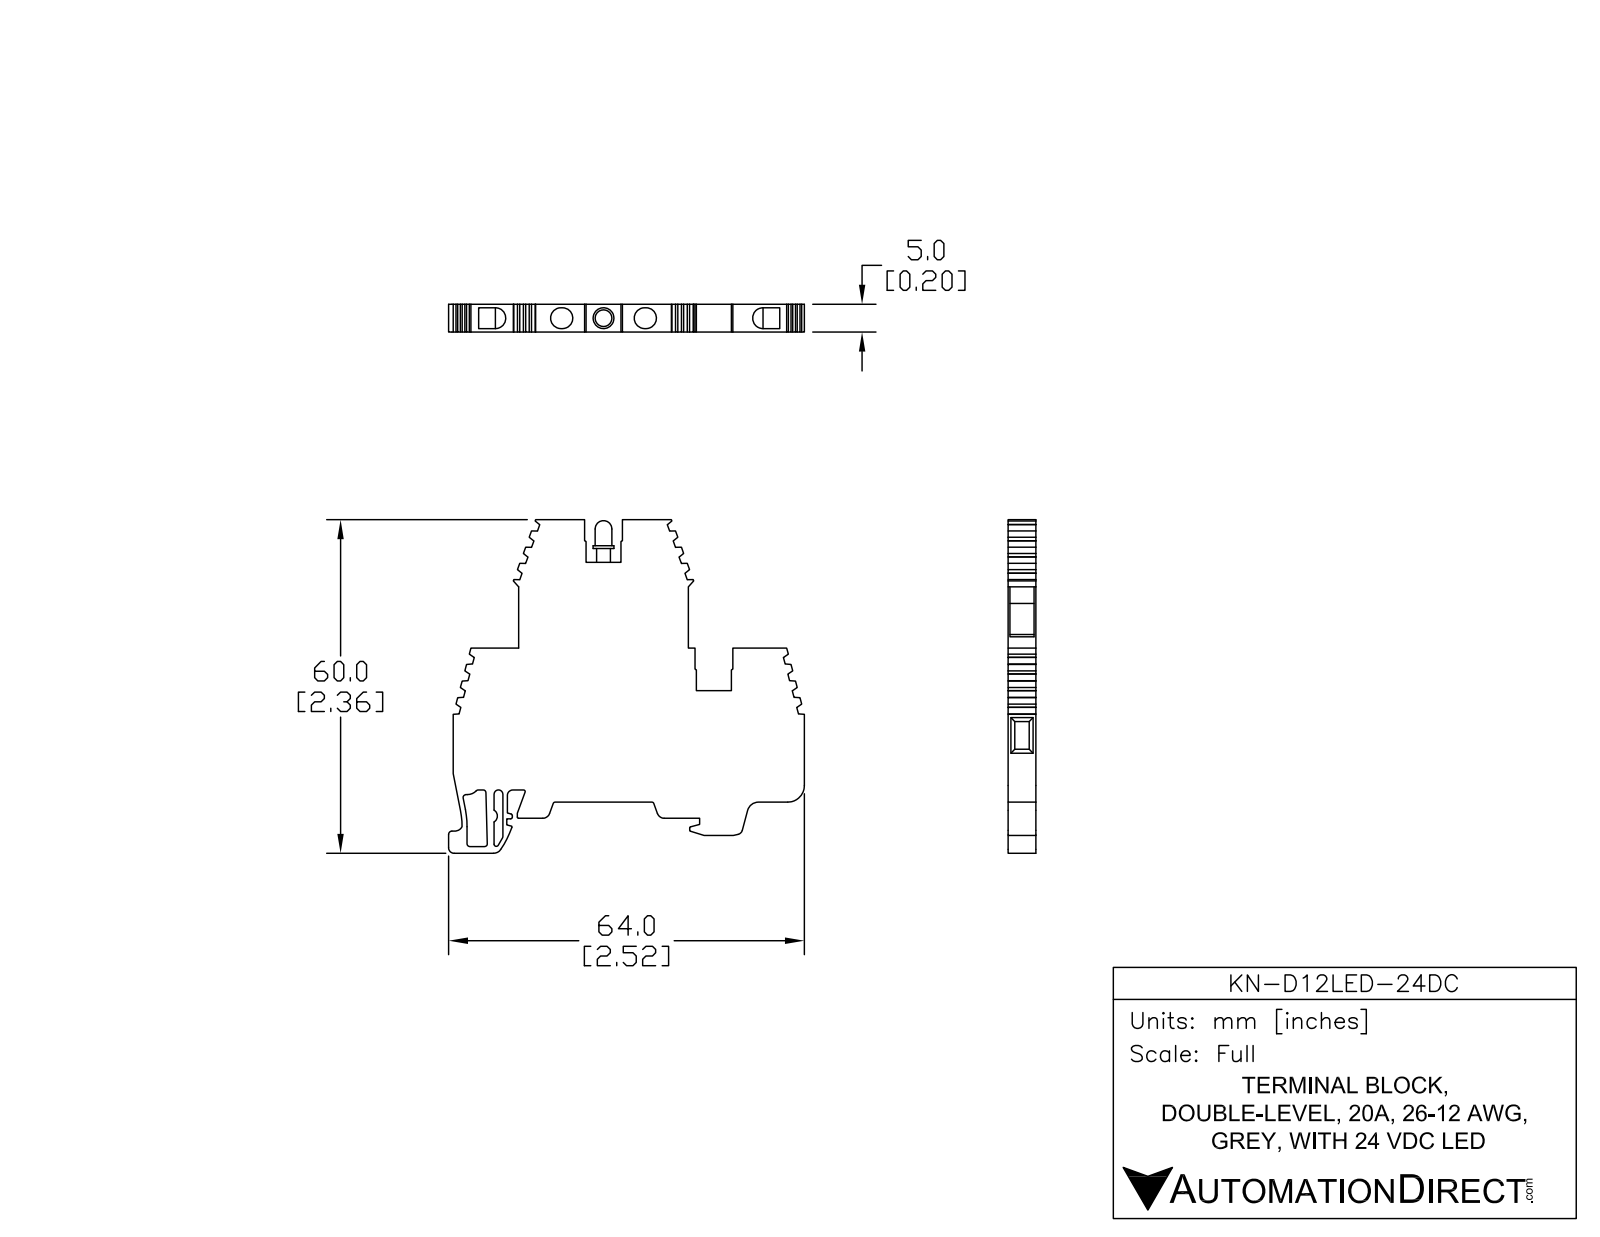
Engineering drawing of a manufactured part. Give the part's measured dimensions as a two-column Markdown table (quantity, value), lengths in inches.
| quantity | value |
| --- | --- |
| part name | KN-D12LED-24DC |
| STEP written by | SolidWorks 2014 (AUTOMOTIVE_DESIGN) |
| units | inches |
| bodies | 3 solids, 250 faces (200 planar, 49 cylindrical, 1 other) |
| overall size | 2.521 × 2.362 × 0.197 |
| volume | 0.696 in³ |
| surface area | 11.04 in² |
| round bosses / shafts (diameter × count) | 0.148 × 1, 0.118 × 1, 0.098 × 1 |
| partial cylindrical surfaces (radius × count) | 0.02 × 7, 0.012 × 6, 0.074 × 6, 0.008 × 3, 0.039 × 3, 0.024 × 2, 0.016 × 1, 0.031 × 1 |
| main face-to-face distances | 0.197, 0.184, 0.013, 0.115, 0.909, 0.157, 0.258, 0.782, 0.248, 0.302 |
